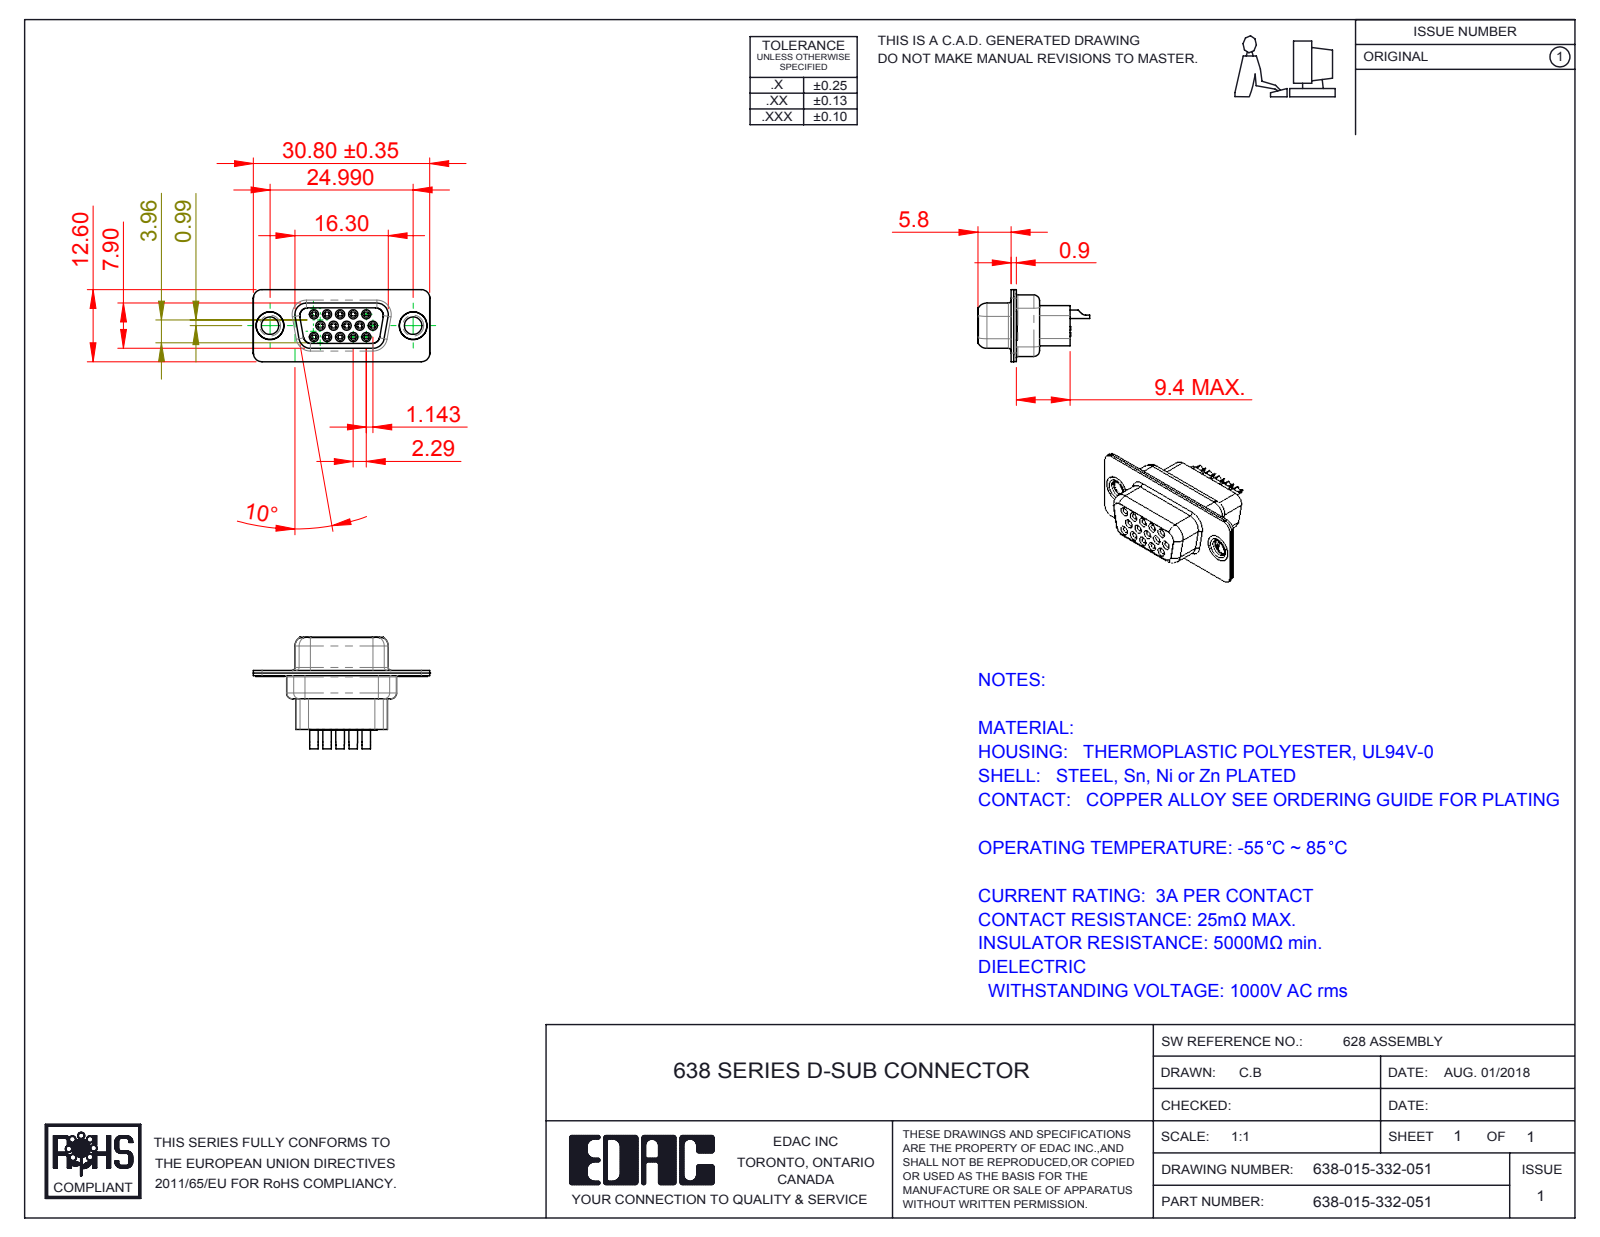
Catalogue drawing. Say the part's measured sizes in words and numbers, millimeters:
The part is named "638 Shell Rear_15 Contacts; 638 Shell Front_15 Contacts; 638 Contact Row 1_32H; 638 Housing_15 Contacts HP (+4 more)". Its 3-D file was written by "SolidWorks 2016 (CONFIG_CONTROL_DESIGN)". It is 20 solids with 1588 faces: 382 planar, 496 cylindrical and 710 other. Overall it measures 30.81 by 19.5 by 12.6 millimeters. Its volume is 1 787 cubic millimeters and its surface area 6 168 square millimeters. Round holes: 15 of diameter 0.8, 15 of diameter 1, 15 of diameter 1.1, 15 of diameter 1.6, 15 of diameter 1.7, 15 of diameter 1.8, 2 of diameter 2, 2 of diameter 3.05, 2 of diameter 4, 2 of diameter 4.05, 2 of diameter 4.85. Round bosses or shafts: 15 of diameter 2, 15 of diameter 1.5, 15 of diameter 1.2, 2 of diameter 5, 2 of diameter 4.95, 2 of diameter 4.8, 2 of diameter 3.55. Partial cylindrical surfaces (rounded edges, fillets, slot ends): 20 of radius 1.5, 12 of radius 2, 10 of radius 0.28, 8 of radius 1.55, 7 of radius 1, 5 of radius 1.35, 4 of radius 0.25, 4 of radius 0.5. The main face-to-face distances are 0.45, 0.9, 0.4, 1.43, 8.88, 6.6, 7, 2.28, 6.2, 9.4. The hole center spacings are 3.96, 2.28, 4.57, 2.29, 6.05, 6.04, 6.86, 7.92.
